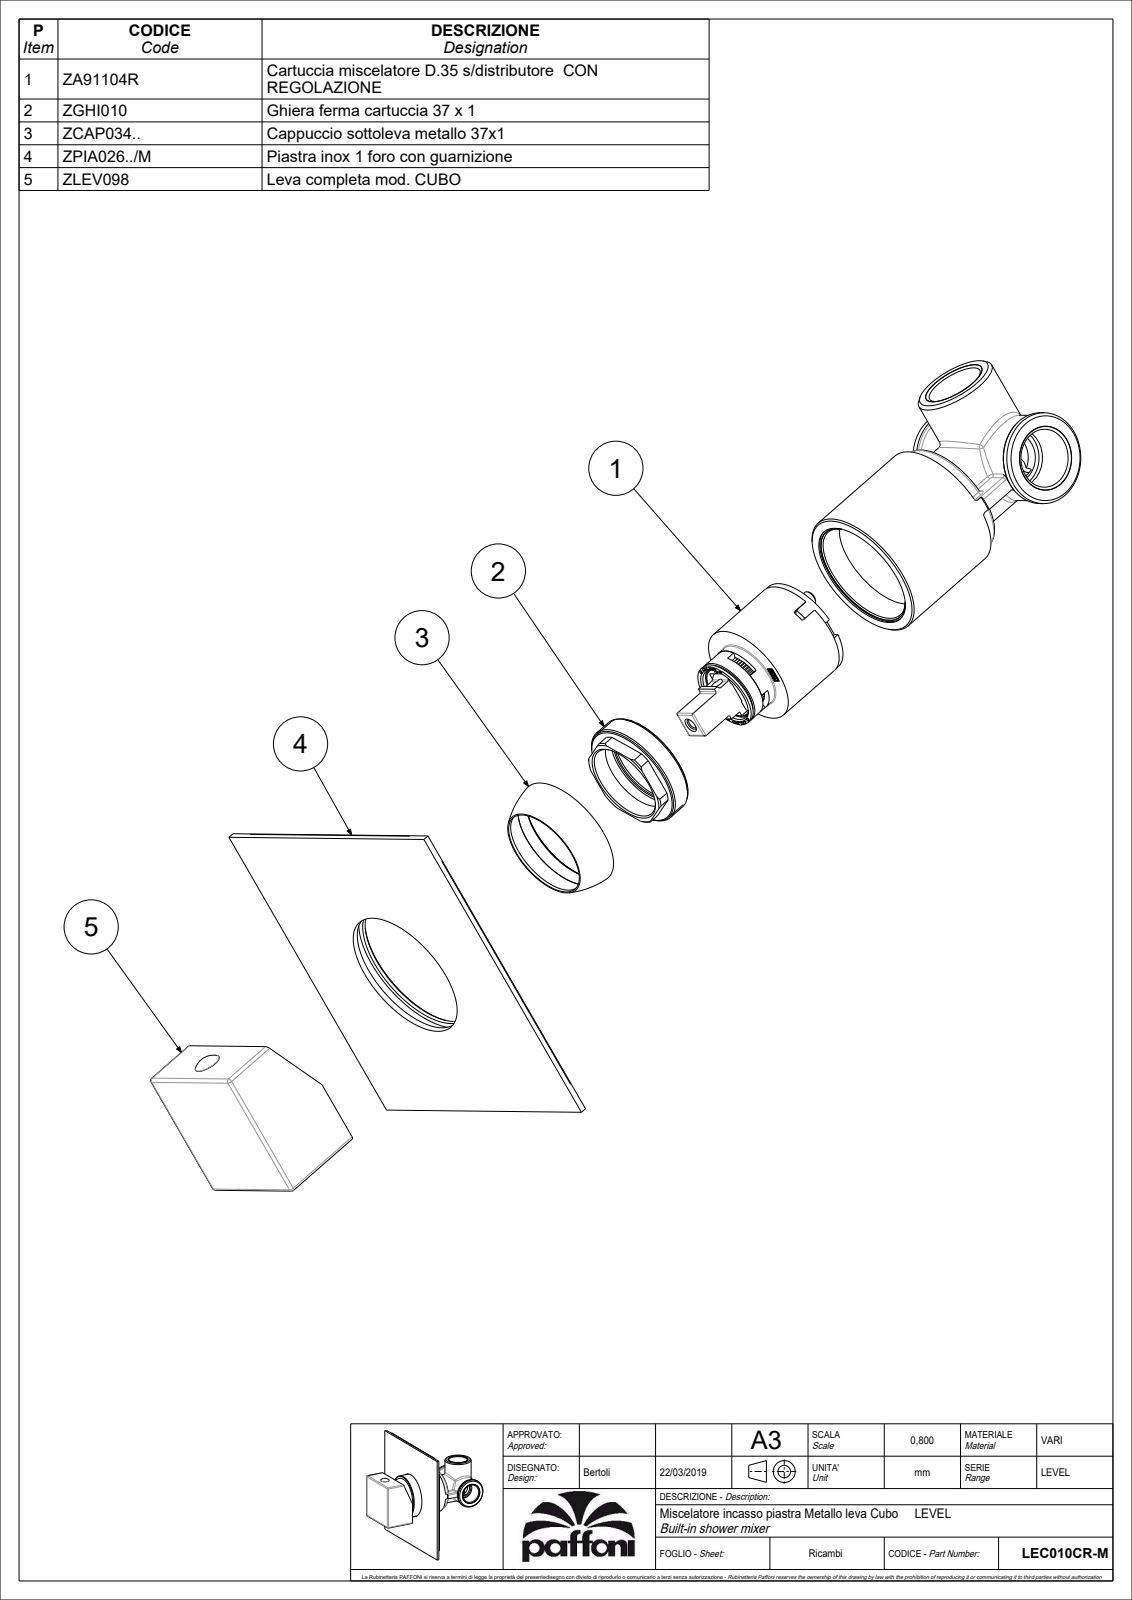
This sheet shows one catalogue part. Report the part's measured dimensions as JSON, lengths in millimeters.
{"part_name": "LEC010CR-M", "step_written_by": "CREO PARAMETRIC BY PTC INC, 2020044 (CONFIG_CONTROL_DESIGN)", "units": "millimeters", "bodies": {"solids": 2, "faces": 842, "planar": 544, "cylindrical": 180, "other": 118}, "overall_size": [110, 110, 48.1], "volume_mm3": 66187, "surface_area_mm2": 52871, "round_holes": [[4, 2], [3.3, 1], [5, 1], [6, 1], [11, 1], [19.5, 1], [19.9, 1], [26.8, 1], [29, 1], [31, 1], [32.4, 1], [36, 1]], "round_bosses_or_shafts": [[44.8, 1], [35, 1], [23.5, 1], [23.4, 1], [21.8, 1], [18, 1], [15, 1], [8, 1]], "partial_cylinders_radius": [[0.15, 11], [1, 10], [0.5, 6], [0.3, 4], [3.95, 1], [7, 1], [9.3, 1], [10.85, 1]], "face_to_face_distances": [2, 45, 48.1, 46.1, 3, 27, 32.5, 45.1, 43.1, 9], "hole_center_spacings": [14.1]}
